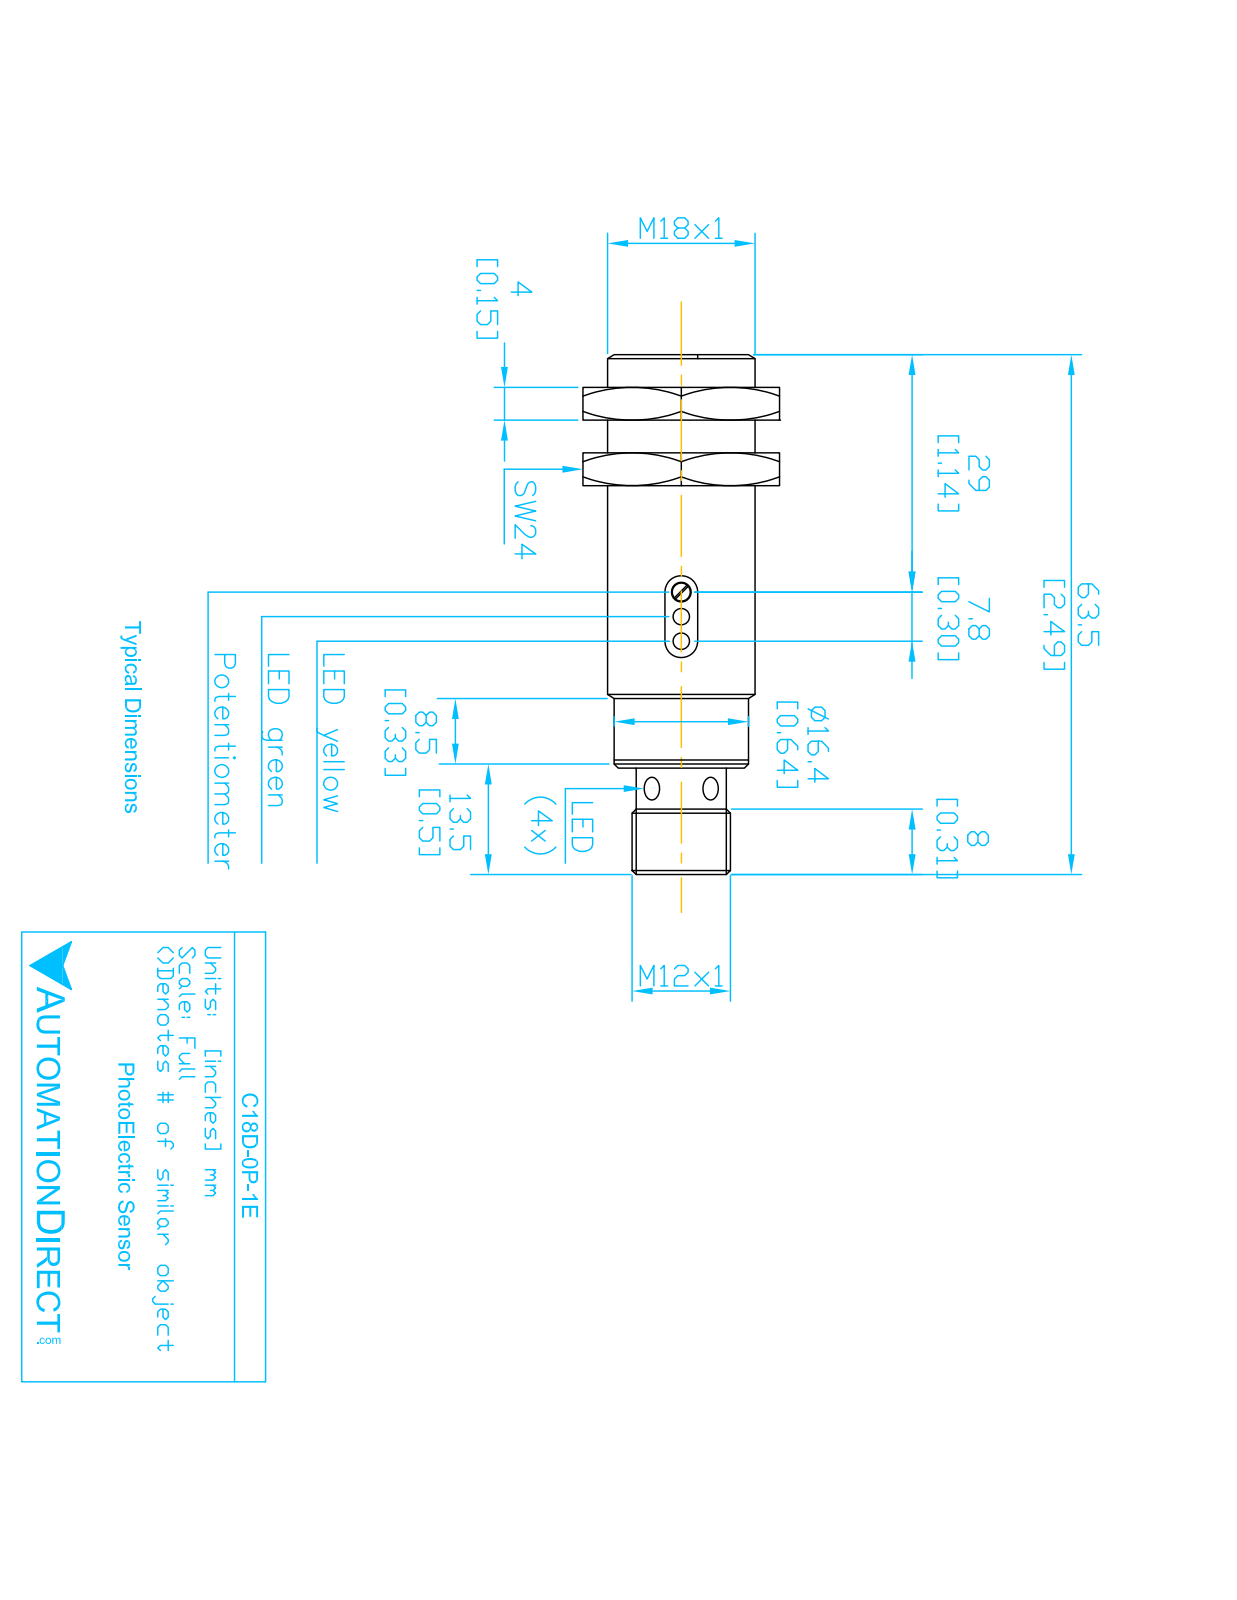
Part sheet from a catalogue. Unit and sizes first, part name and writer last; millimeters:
Units: millimetres
Overall size (bounding box): 63.5 × 18 × 18
Round holes (diameter × count): ⌀3 ×2, ⌀8.5 ×1
Round bosses / shafts (diameter × count): ⌀1 ×4, ⌀18 ×1, ⌀16.4 ×1, ⌀15.7 ×1, ⌀11.7 ×1, ⌀10.5 ×1
Partial cylindrical surfaces — rounded edges, fillets, slot ends (radius × count): R0.5 ×3, R5.1 ×1
Main face-to-face distances: 50.5, 2.5, 48, 2.3, 50.3, 54.8, 54.6, 52.3, 4.3, 63.5
Volume: 13 500 mm³ · Surface area: 5 156 mm²
Bodies: 3 solids, 63 faces (15 planar, 29 cylindrical, 19 other)
Part name (STEP PRODUCT): C18D-0P-1E
STEP written by: SolidWorks 2017 (AUTOMOTIVE_DESIGN)
